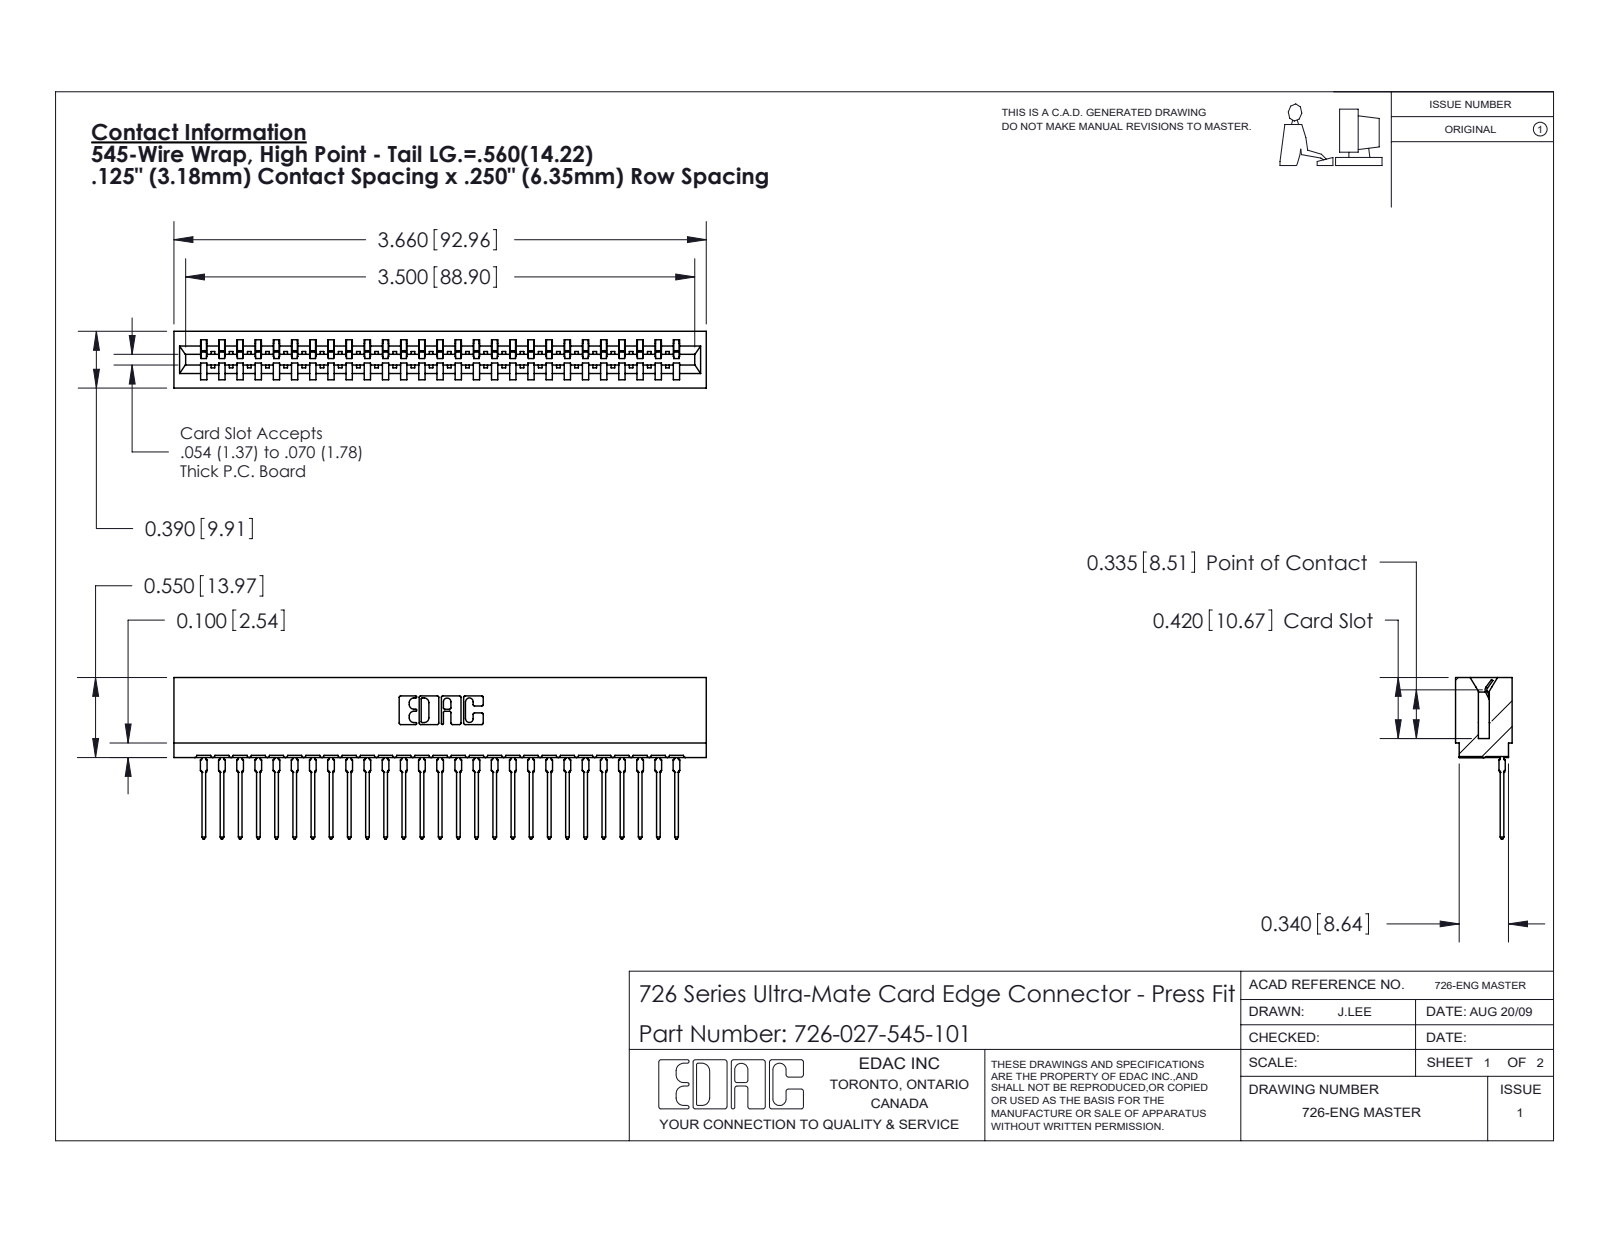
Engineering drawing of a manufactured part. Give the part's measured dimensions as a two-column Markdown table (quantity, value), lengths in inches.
| quantity | value |
| --- | --- |
| part name | 726 Part_.515 Slot Depth - 01; 726-027-545-101; 746-292-001_545 |
| STEP written by | SolidWorks 2020 (CONFIG_CONTROL_DESIGN) |
| units | inches |
| bodies | 28 solids, 3013 faces (1756 planar, 555 cylindrical, 702 other) |
| overall size | 3.66 × 1.109 × 0.39 |
| volume | 0.516 in³ |
| surface area | 20.26 in² |
| partial cylindrical surfaces (radius × count) | 0.021 × 54, 0.015 × 28, 0.01 × 22, 0.007 × 6, 0.031 × 6, 0.005 × 4, 0.011 × 4, 0.026 × 3 |
| main face-to-face distances | 0.057, 0.333, 0.25, 0.39, 0.025, 0.307, 0.083, 0.275, 0.5, 0.365 |
